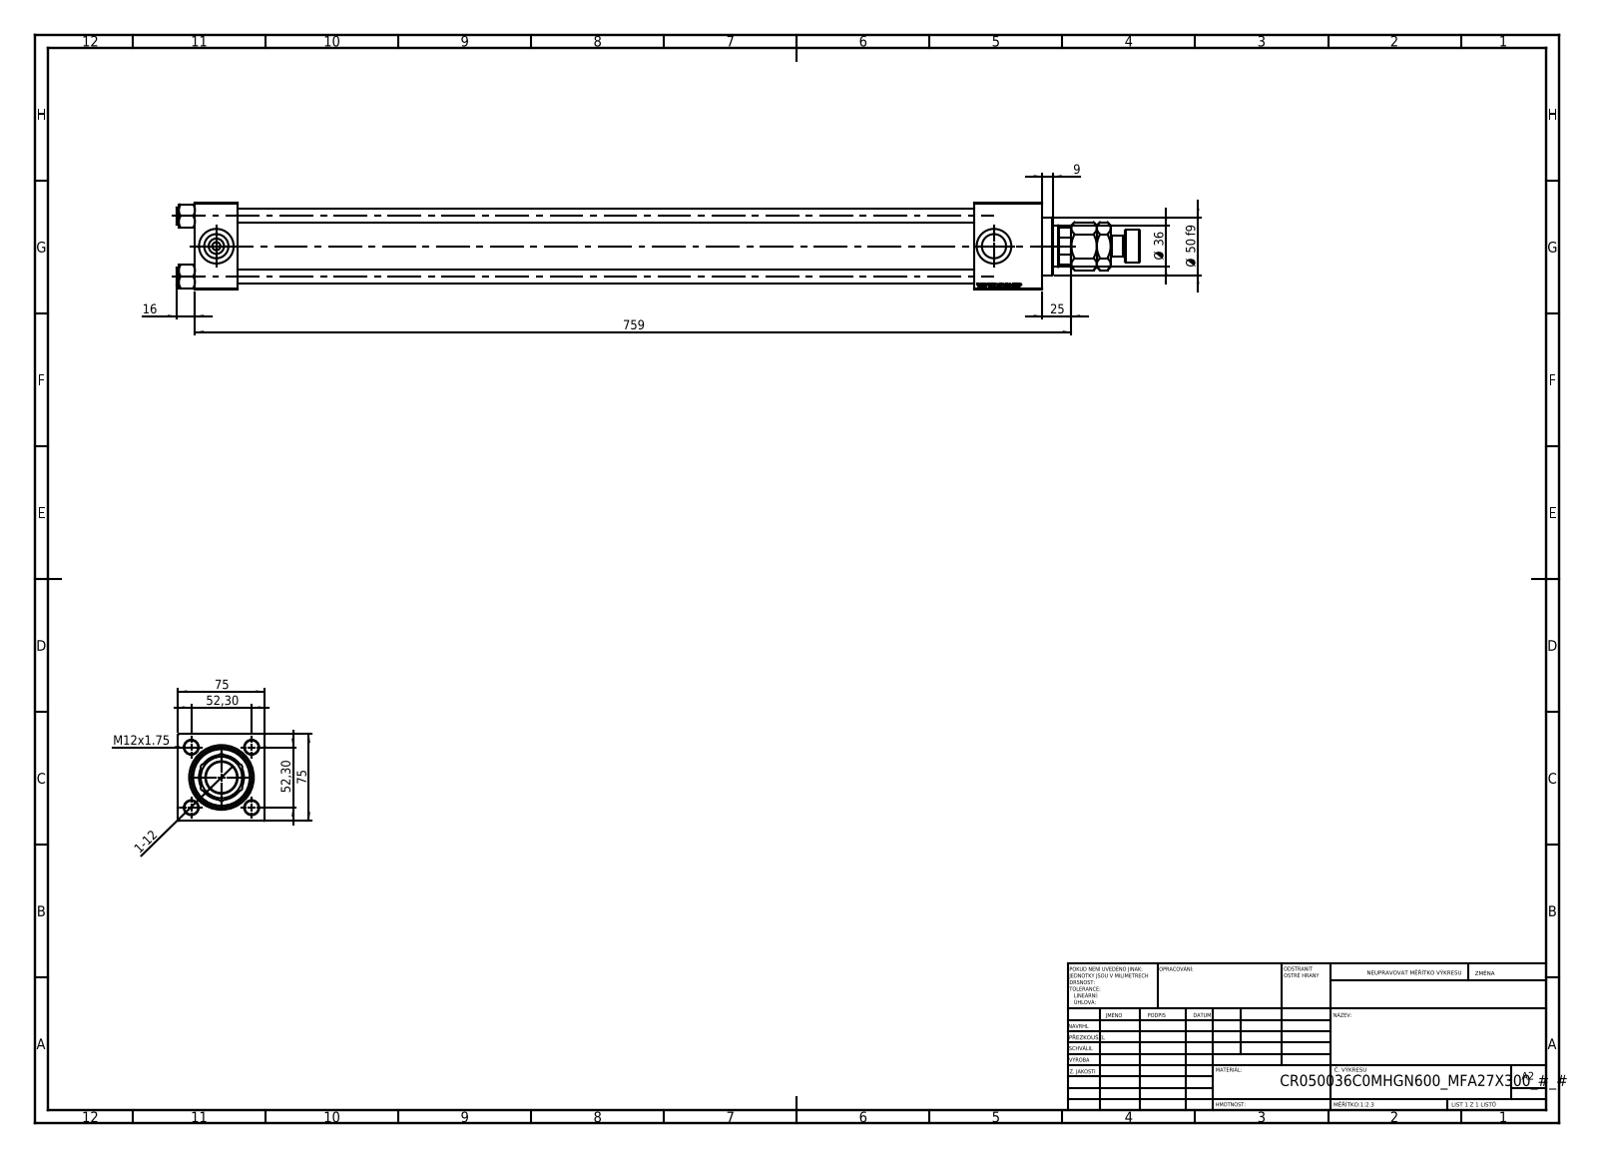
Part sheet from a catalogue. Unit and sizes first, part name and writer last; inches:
Units: inches
Overall size (bounding box): 32.835 × 2.974 × 2.953
Round holes (diameter × count): ⌀0.472 ×4, ⌀0.276 ×2, ⌀0.825 ×2, ⌀1.181 ×2, ⌀1.004 ×1, ⌀1.417 ×1, ⌀1.535 ×1, ⌀1.614 ×1, ⌀2.087 ×1
Round bosses / shafts (diameter × count): ⌀0.591 ×4, ⌀2.205 ×1, ⌀1.969 ×1, ⌀1.102 ×1, ⌀0.709 ×1
Partial cylindrical surfaces — rounded edges, fillets, slot ends (radius × count): R0.689 ×1
Main face-to-face distances: 2.953, 1.457, 2.323, 26.575, 25.118, 28.898, 27.441, 3.307, 0.984, 27.768
Hole centre spacings: 1.456, 2.059, 2.912, 26.516
Volume: 114.5 in³ · Surface area: 791.3 in²
Bodies: 12 solids, 1200 faces (542 planar, 90 cylindrical, 568 other)
Part name (STEP PRODUCT): V215CR_C_TYCINKA; NUT_M5_C; MFA; V215CR_VCP_C (+2 more)
STEP written by: SolidWorks 2019 (CONFIG_CONTROL_DESIGN)
